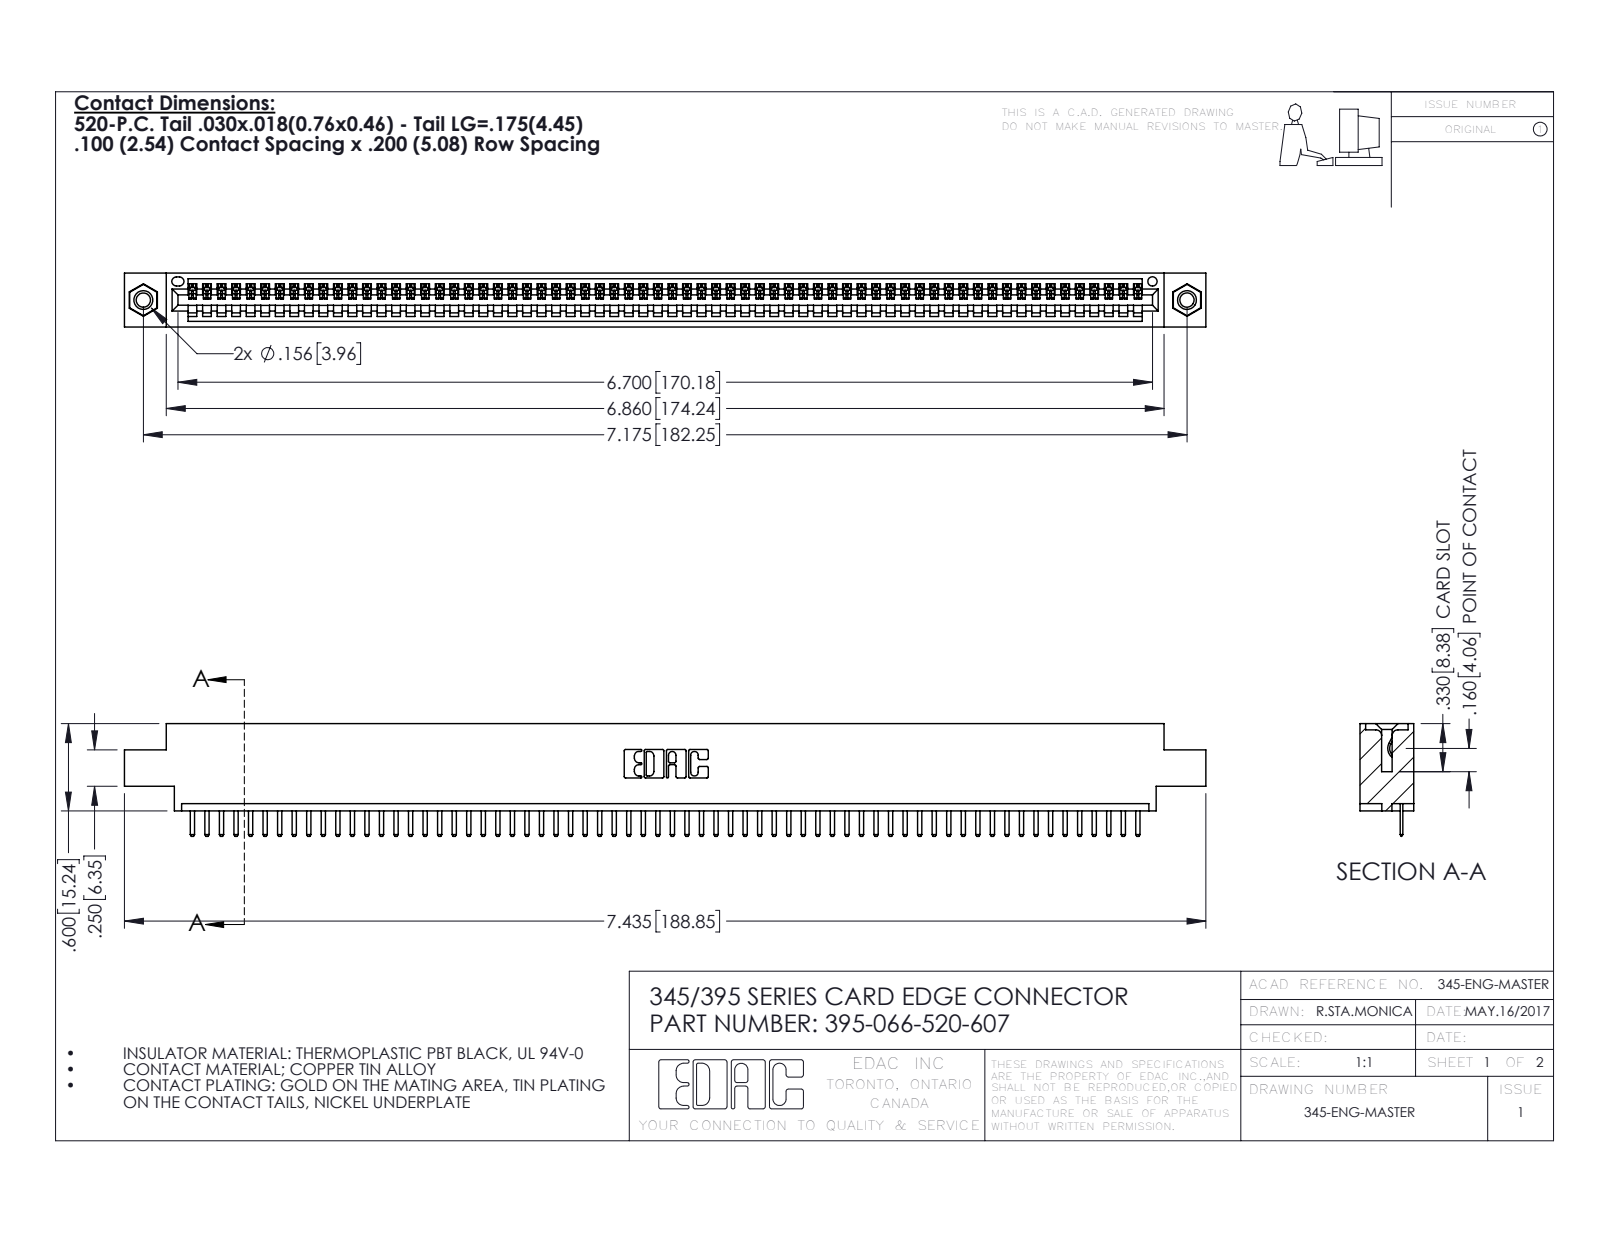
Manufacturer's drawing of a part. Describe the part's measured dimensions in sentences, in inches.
The part is named "345-292-001_345-293-120; 345 Part_0.170 Offset - 0.156 Dia-TI; 395-066-520-607; 345-250-001_345-250-005-103". Its 3-D file was written by "SolidWorks 2016 (CONFIG_CONTROL_DESIGN)". It is 69 solids with 4282 faces: 2888 planar, 1378 cylindrical and 16 other. Overall it measures 7.435 by 0.775 by 0.37 inches. Its volume is 1.087 cubic inches and its surface area 36.49 square inches. Round holes: 2 of diameter 0.098, 2 of diameter 0.125, 2 of diameter 0.156, 1 of diameter 0.064. Round bosses or shafts: 2 of diameter 0.155. Partial cylindrical surfaces (rounded edges, fillets, slot ends): 134 of radius 0.01, 132 of radius 0.006, 22 of radius 0.01, 6 of radius 0.007, 6 of radius 0.031, 3 of radius 0.026, 2 of radius 0.031, 2 of radius 0.04. The main face-to-face distances are 0.072, 0.298, 0.37, 0.2, 0.098, 0.272, 0.025, 0.225, 0.072, 0.175. The hole center spacings are 0.27, 6.939, 7.175.
